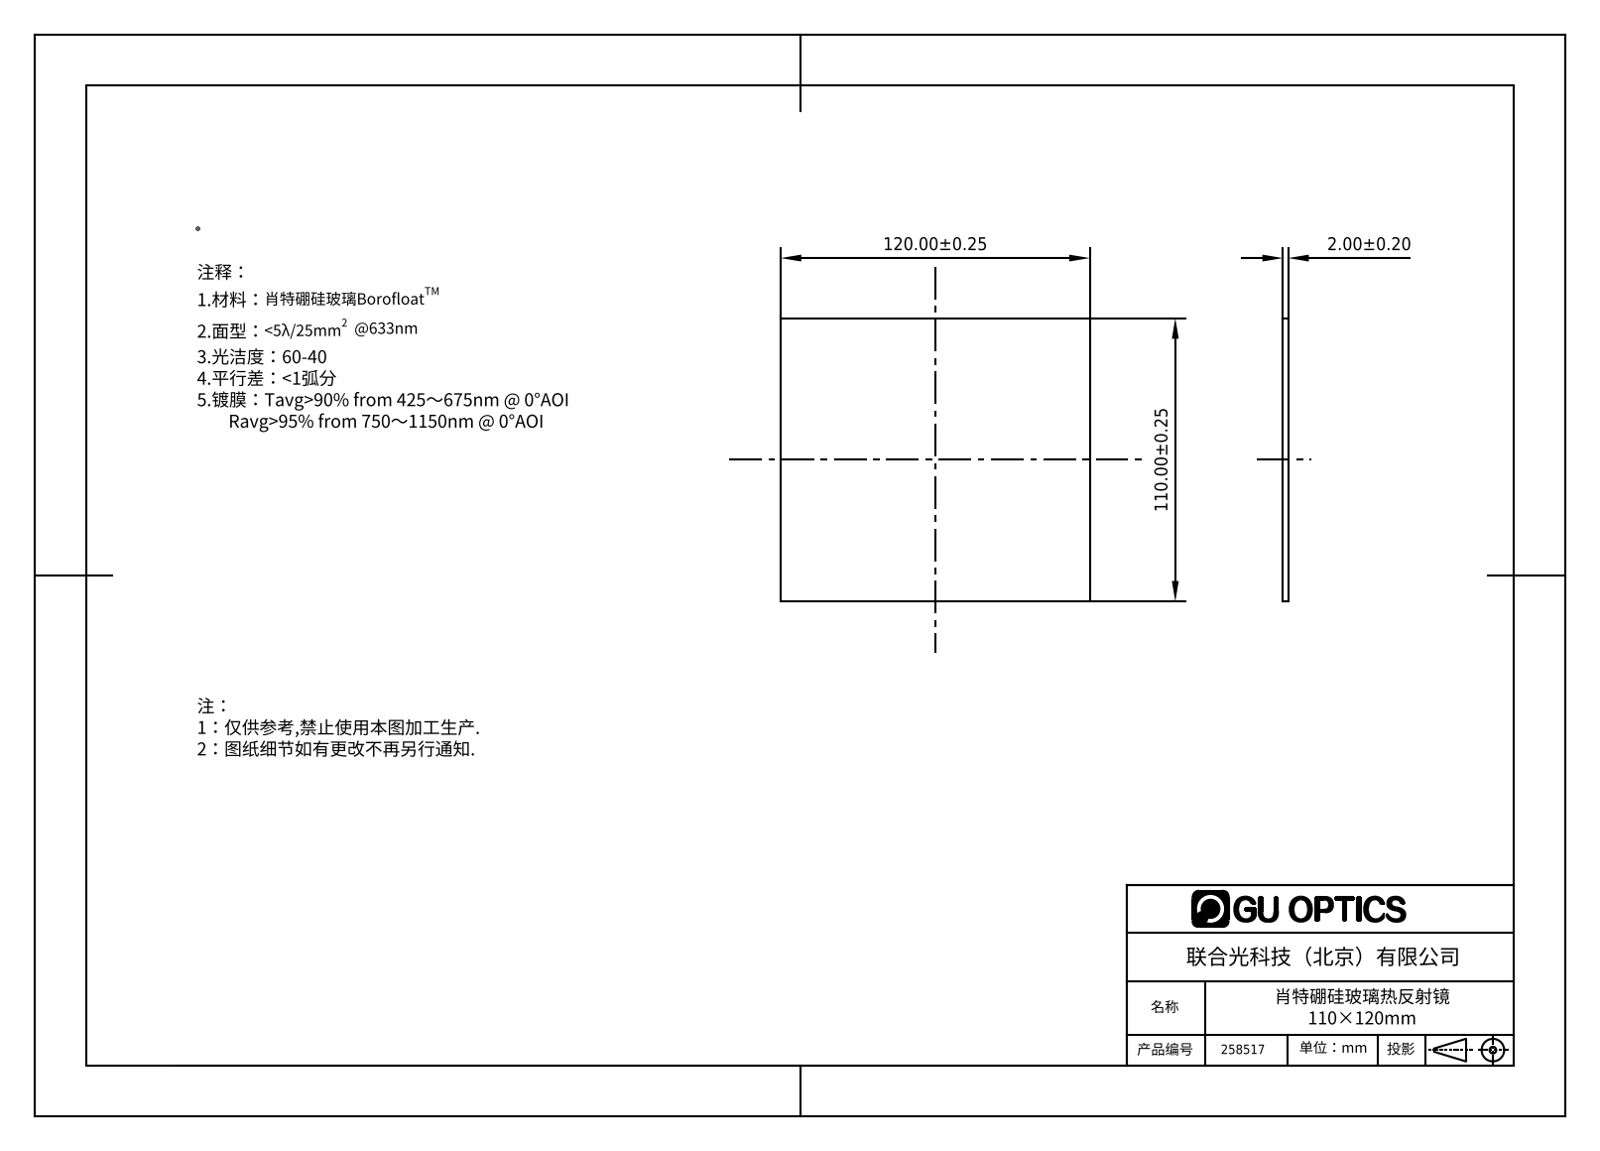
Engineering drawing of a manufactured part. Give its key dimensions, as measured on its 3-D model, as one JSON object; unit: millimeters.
{"part_name": "258517", "step_written_by": "SolidWorks 2016 (AUTOMOTIVE_DESIGN)", "units": "millimeters", "bodies": {"solids": 1, "faces": 6, "planar": 6, "cylindrical": 0, "other": 0}, "overall_size": [120, 110, 2], "volume_mm3": 26400, "surface_area_mm2": 27320, "face_to_face_distances": [2, 110, 120]}
